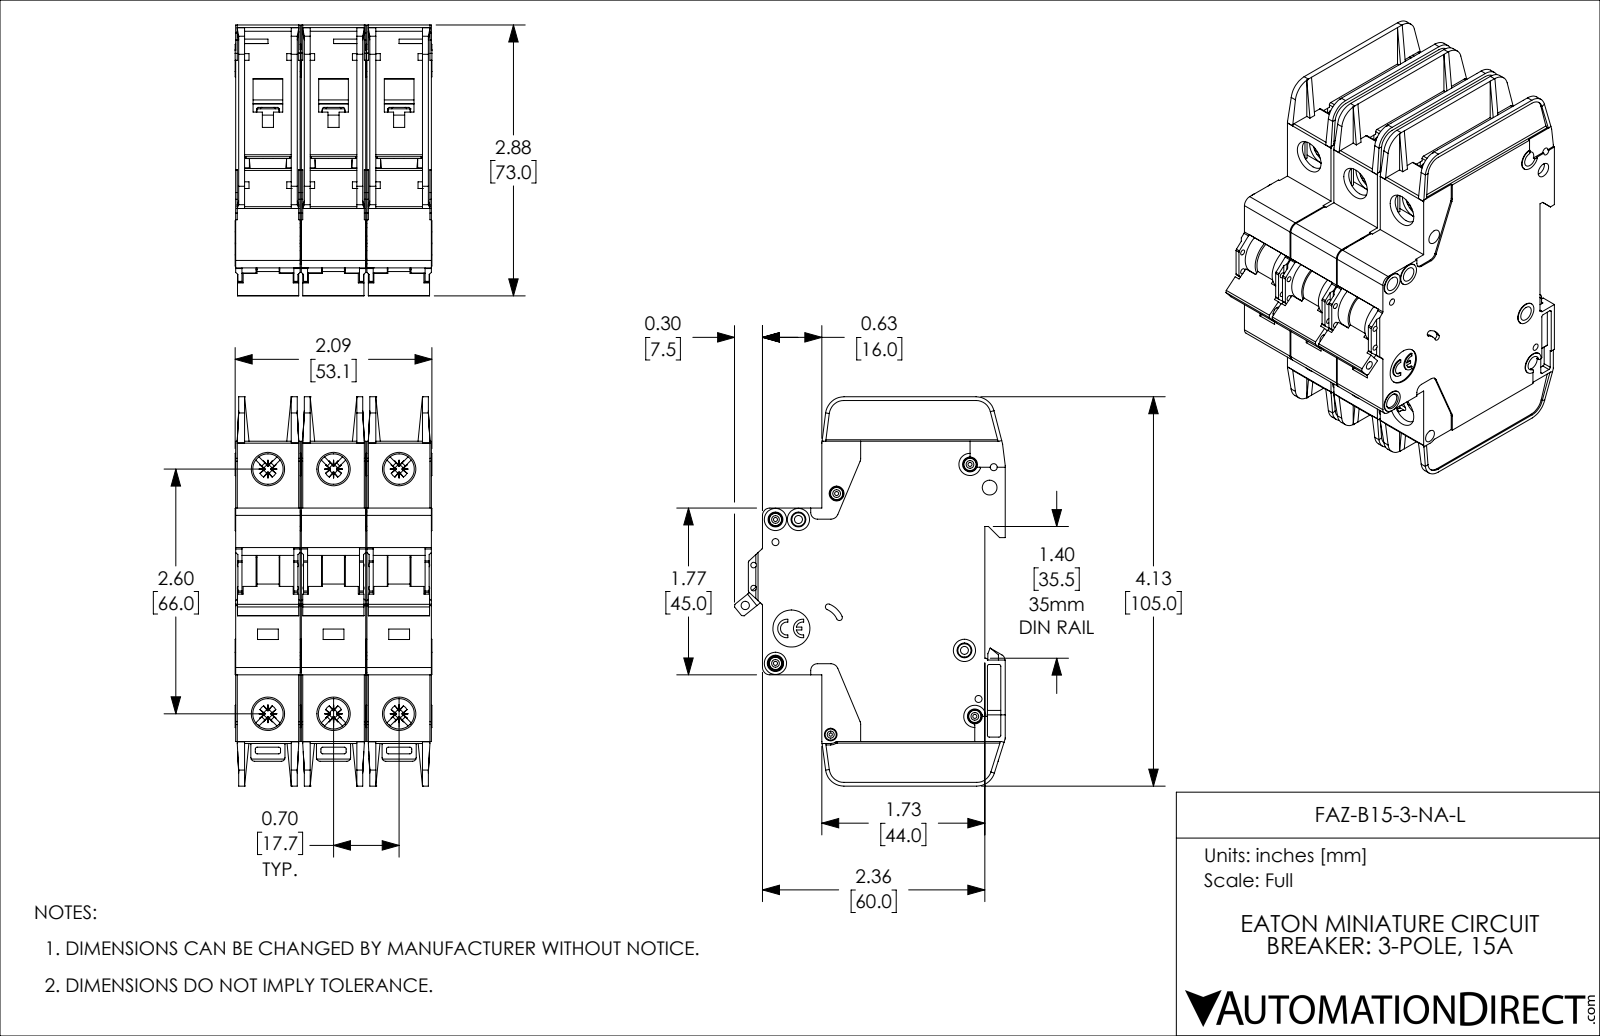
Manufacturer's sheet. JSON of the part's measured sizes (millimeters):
{"part_name": "FAZ-B15-3-NA-L", "step_written_by": "SolidWorks 2019 (AUTOMOTIVE_DESIGN)", "units": "millimeters", "bodies": {"solids": 3, "faces": 3381, "planar": 2013, "cylindrical": 1071, "other": 297}, "overall_size": [105, 73.1, 53.1], "volume_mm3": 230200, "surface_area_mm2": 79350, "round_holes": [[4, 8], [8.2, 6], [1.1, 5], [1.9, 4], [1.5, 2], [2.2, 2], [0.9, 1], [2.3, 1], [2.5, 1], [3.4, 1], [10, 1]], "round_bosses_or_shafts": [[3.3, 5], [6, 4], [3, 4], [2.5, 3]], "partial_cylinders_radius": [[0.5, 72], [0.4, 30], [1, 18], [1.1, 12], [2, 12], [0.2, 6], [0.3, 6], [0.7, 6]], "face_to_face_distances": [17.7, 1.2, 35.4, 17.4, 15, 35.1, 18.9, 16.5, 2.7, 2.4], "hole_center_spacings": [17.7, 68.3, 66, 6.2, 13.6, 22.1, 35.4, 74.9]}
